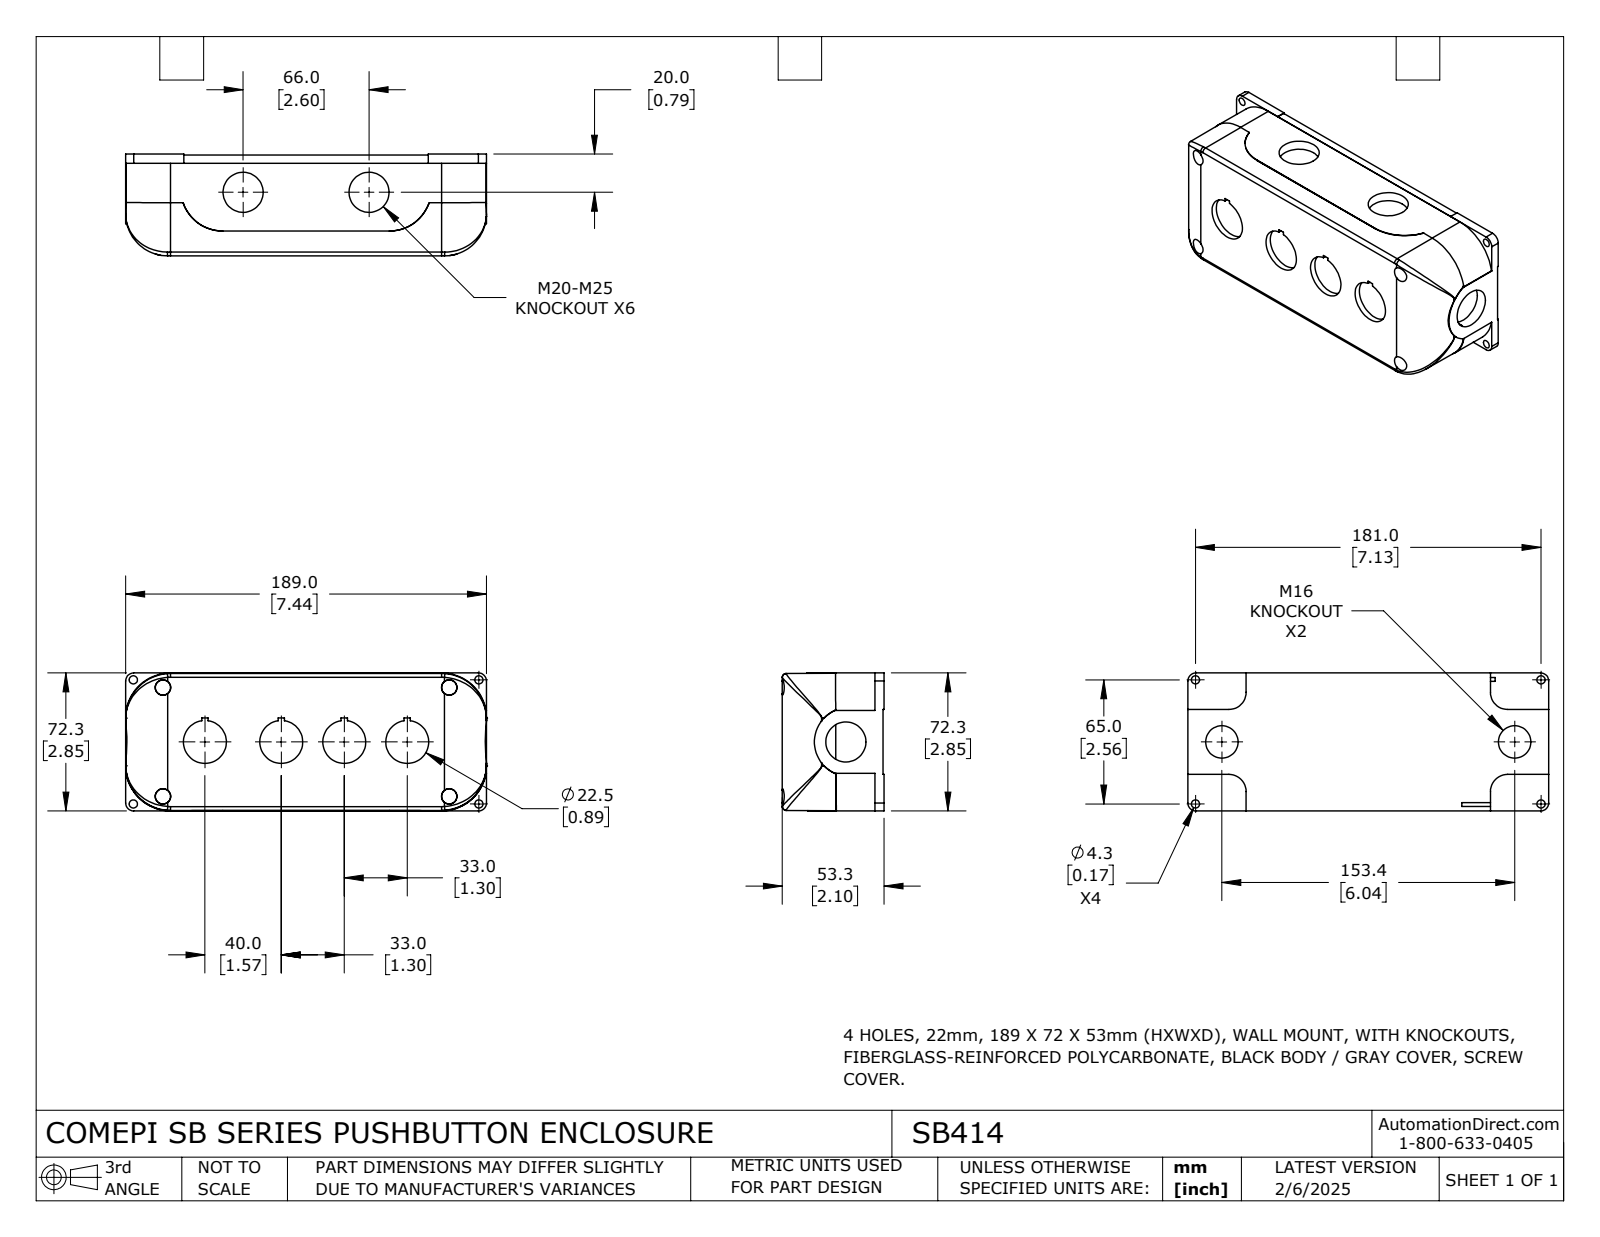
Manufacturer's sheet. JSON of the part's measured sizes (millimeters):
{"part_name": "SB414", "step_written_by": "SolidWorks 2024 (CONFIG_CONTROL_DESIGN)", "units": "millimeters", "bodies": {"solids": 2, "faces": 341, "planar": 169, "cylindrical": 90, "other": 82}, "overall_size": [189, 72.3, 53.3], "volume_mm3": 350000, "surface_area_mm2": 100600, "round_holes": [[4.3, 4], [22.5, 4], [21, 3], [17, 2]], "partial_cylinders_radius": [[0.9, 4], [2, 4], [4, 4], [9, 4], [9.7, 4], [22, 4], [23.6, 4], [20, 2]], "face_to_face_distances": [2.5, 52.8, 50.3, 39.8, 37.3, 13, 60.8, 66.5, 5.7, 5.7], "hole_center_spacings": [35.3, 49.6, 147.1, 170.3, 23.7, 33, 65, 66]}
